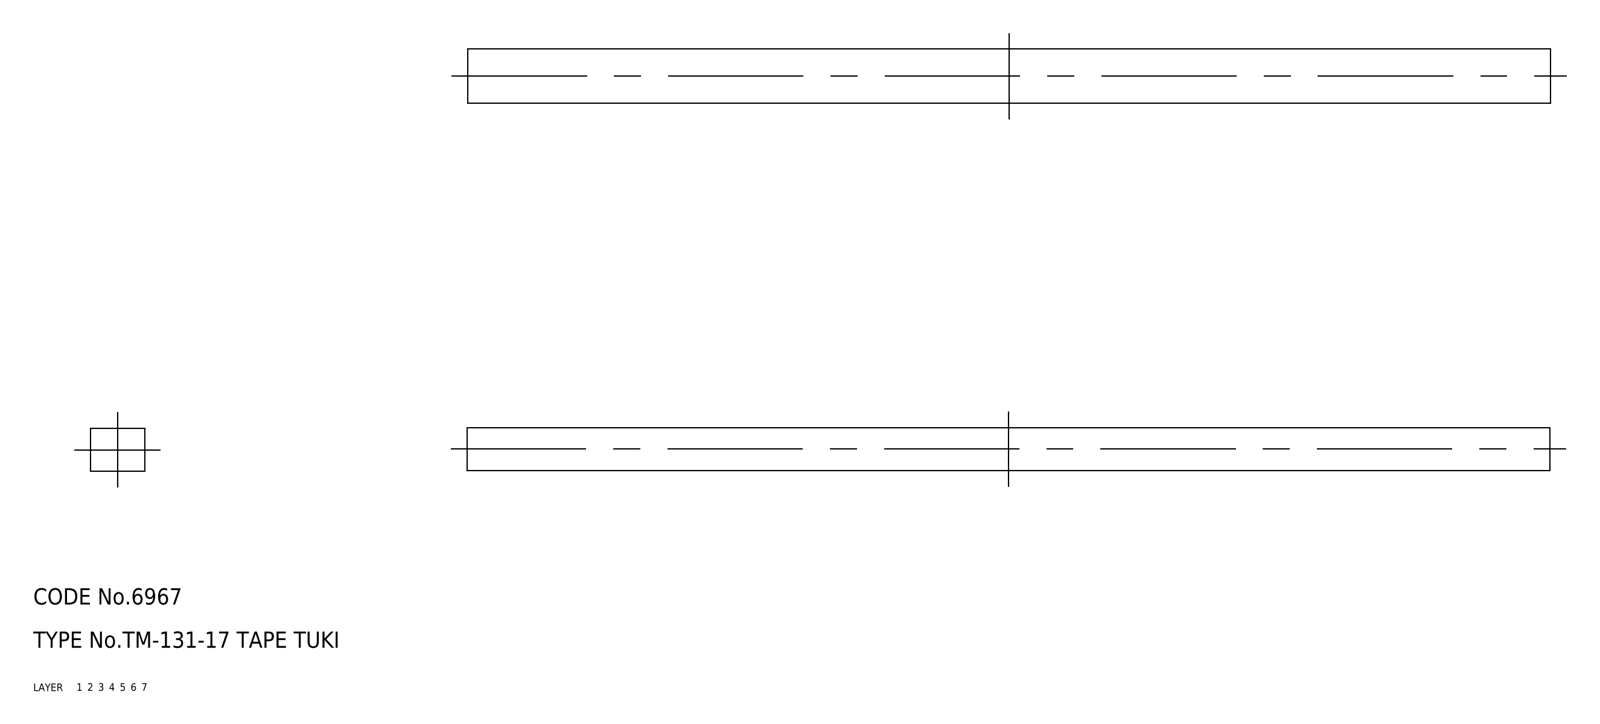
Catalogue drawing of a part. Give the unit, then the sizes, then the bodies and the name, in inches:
Units: inches
Overall size (bounding box): 7.874 × 0.394 × 0.315
Volume: 0.976 in³ · Surface area: 11.41 in²
Bodies: 1 solid, 6 faces (0 planar, 0 cylindrical, 6 other)
Part name (STEP PRODUCT): rubber foam
STEP written by: CADfix (AUTOMOTIVE_DESIGN)
